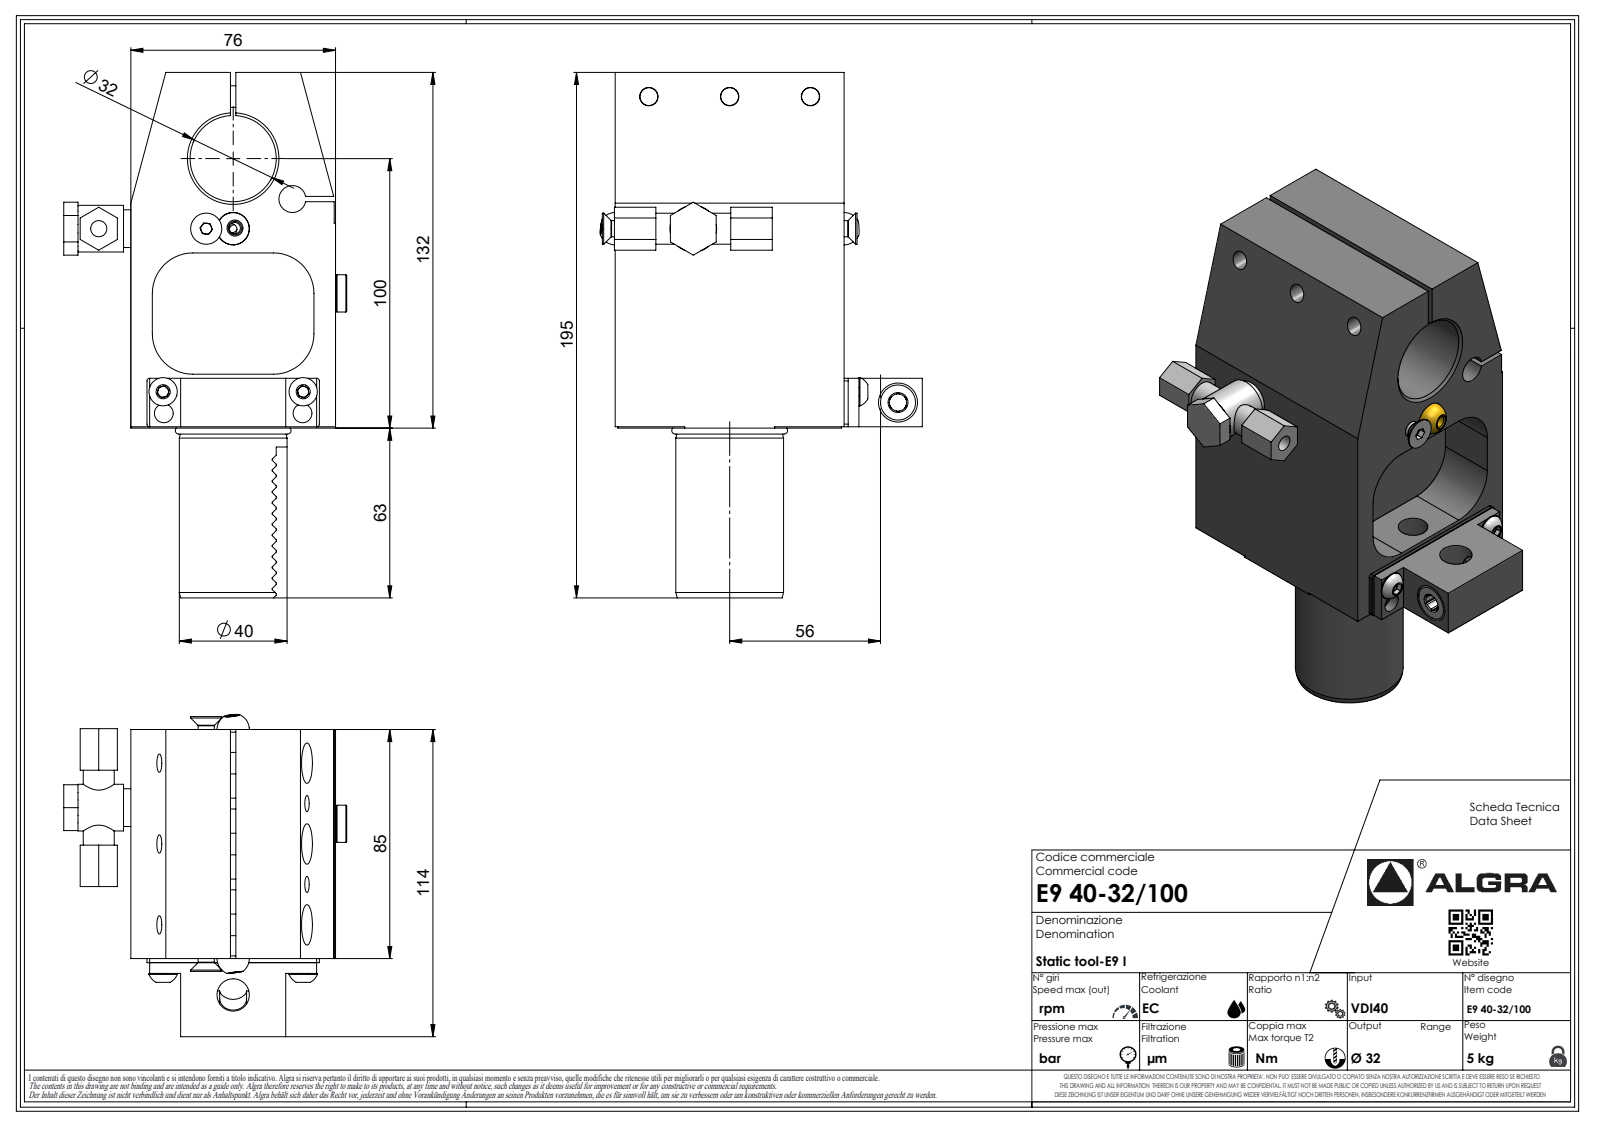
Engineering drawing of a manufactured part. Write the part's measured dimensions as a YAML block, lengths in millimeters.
part_name: "E940-32100"
step_written_by: "SolidWorks 2023 (AUTOMOTIVE_DESIGN)"
units: millimeters
bodies: {solids: 1, faces: 381, planar: 244, cylindrical: 64, other: 73}
overall_size: [195, 119.6, 80.15]
volume: 709540
surface_area: 85529
round_holes:
  - {diameter: 2.1, count: 1}
  - {diameter: 10, count: 1}
  - {diameter: 32, count: 1}
round_bosses_or_shafts:
  - {diameter: 8, count: 3}
  - {diameter: 4, count: 2}
  - {diameter: 40, count: 1}
  - {diameter: 38.7, count: 1}
  - {diameter: 13.8, count: 1}
  - {diameter: 12, count: 1}
  - {diameter: 6.37, count: 1}
  - {diameter: 1.7, count: 1}
partial_cylinders:
  - {radius: 0.3, count: 13}
  - {radius: 0.33, count: 7}
  - {radius: 0.52, count: 7}
  - {radius: 3.7, count: 7}
  - {radius: 1, count: 4}
  - {radius: 15, count: 4}
  - {radius: 0.21, count: 1}
  - {radius: 41.5, count: 1}
face_to_face_distances: [76, 63, 22, 85, 132, 0.5, 18.5, 39, 68, 131.5]
hole_center_spacings: [26.63]
